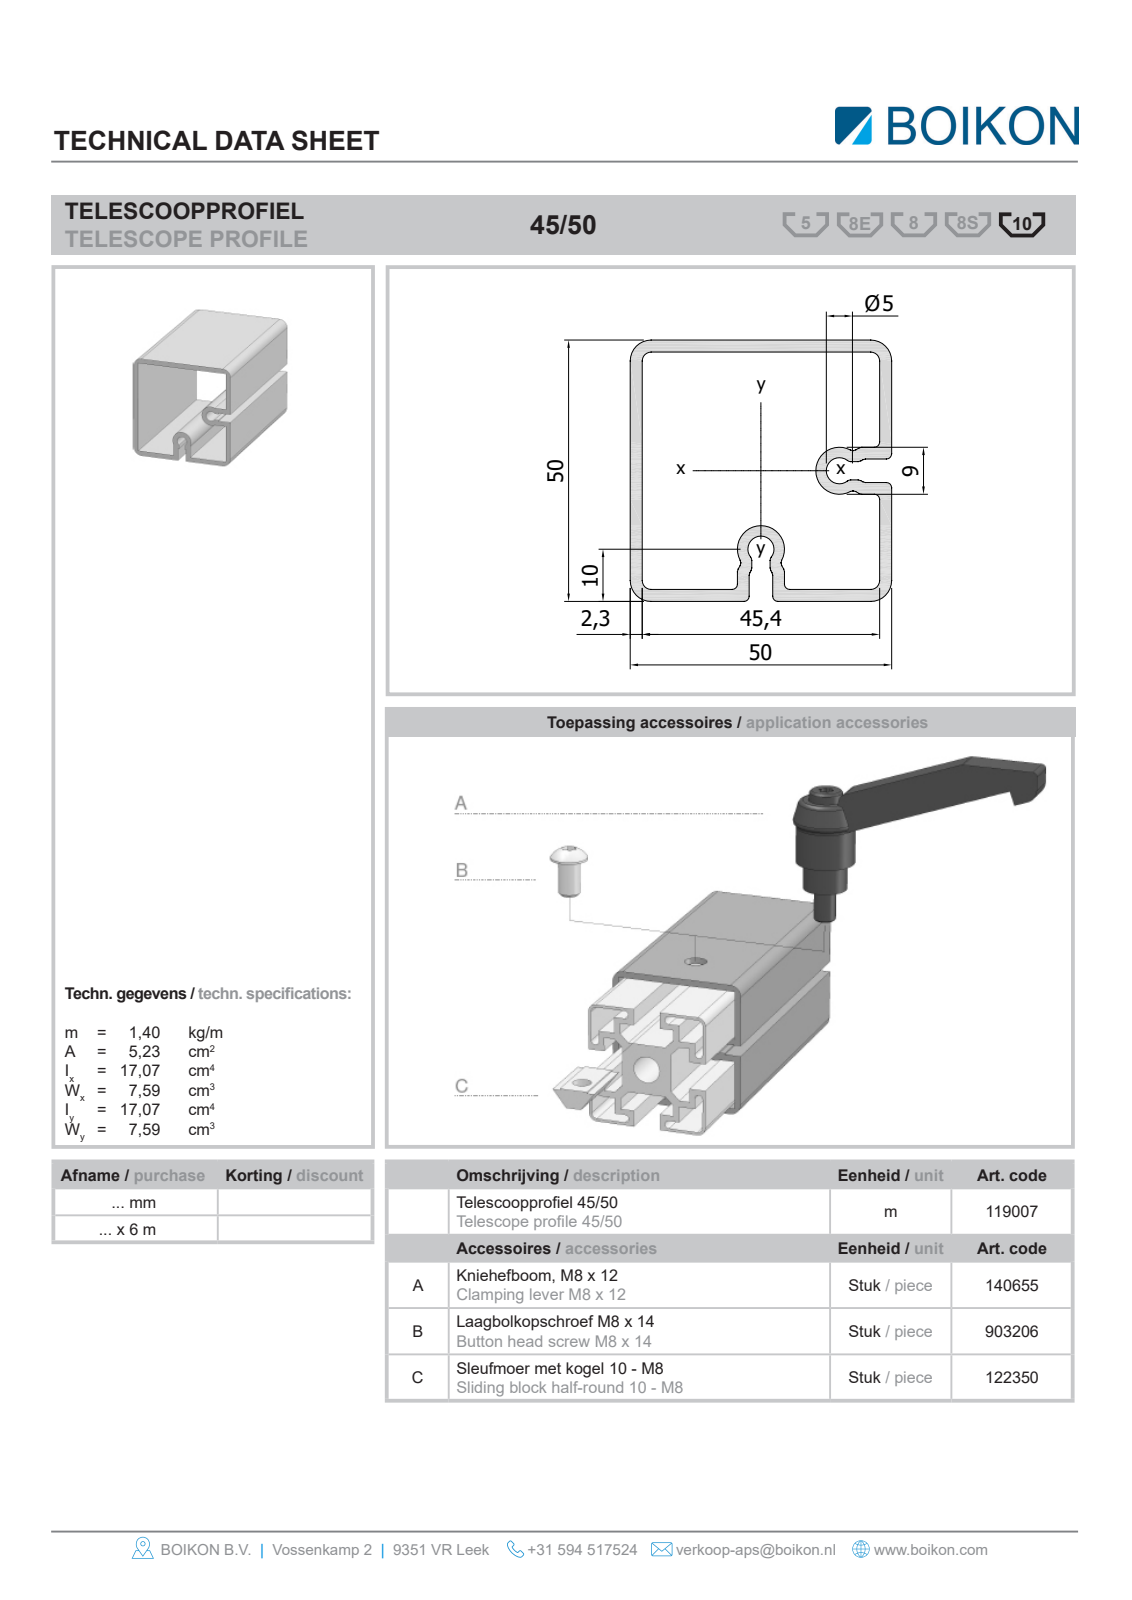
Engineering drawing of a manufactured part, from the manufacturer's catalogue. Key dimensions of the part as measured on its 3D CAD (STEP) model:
Part name (STEP PRODUCT): Root; 119007Telescoopprofiel 45/50BOIKON0
STEP written by: HiCAD 2013 1802.4 Build 509 (AUTOMOTIVE_DESIGN)
Units: millimetres
Bodies: 1 solid, 38 faces (30 planar, 8 cylindrical, 0 other)
Overall size (bounding box): 1000 × 50 × 50
Volume: 534 543 mm³ · Surface area: 470 012 mm²
Partial cylindrical surfaces — rounded edges, fillets, slot ends (radius × count): R4 ×4, R2.5 ×2, R4.8 ×2
Main face-to-face distances: 2.3, 47.7, 50, 45.4, 27.05, 20.65, 22.95, 24.75, 29.35, 18.35
